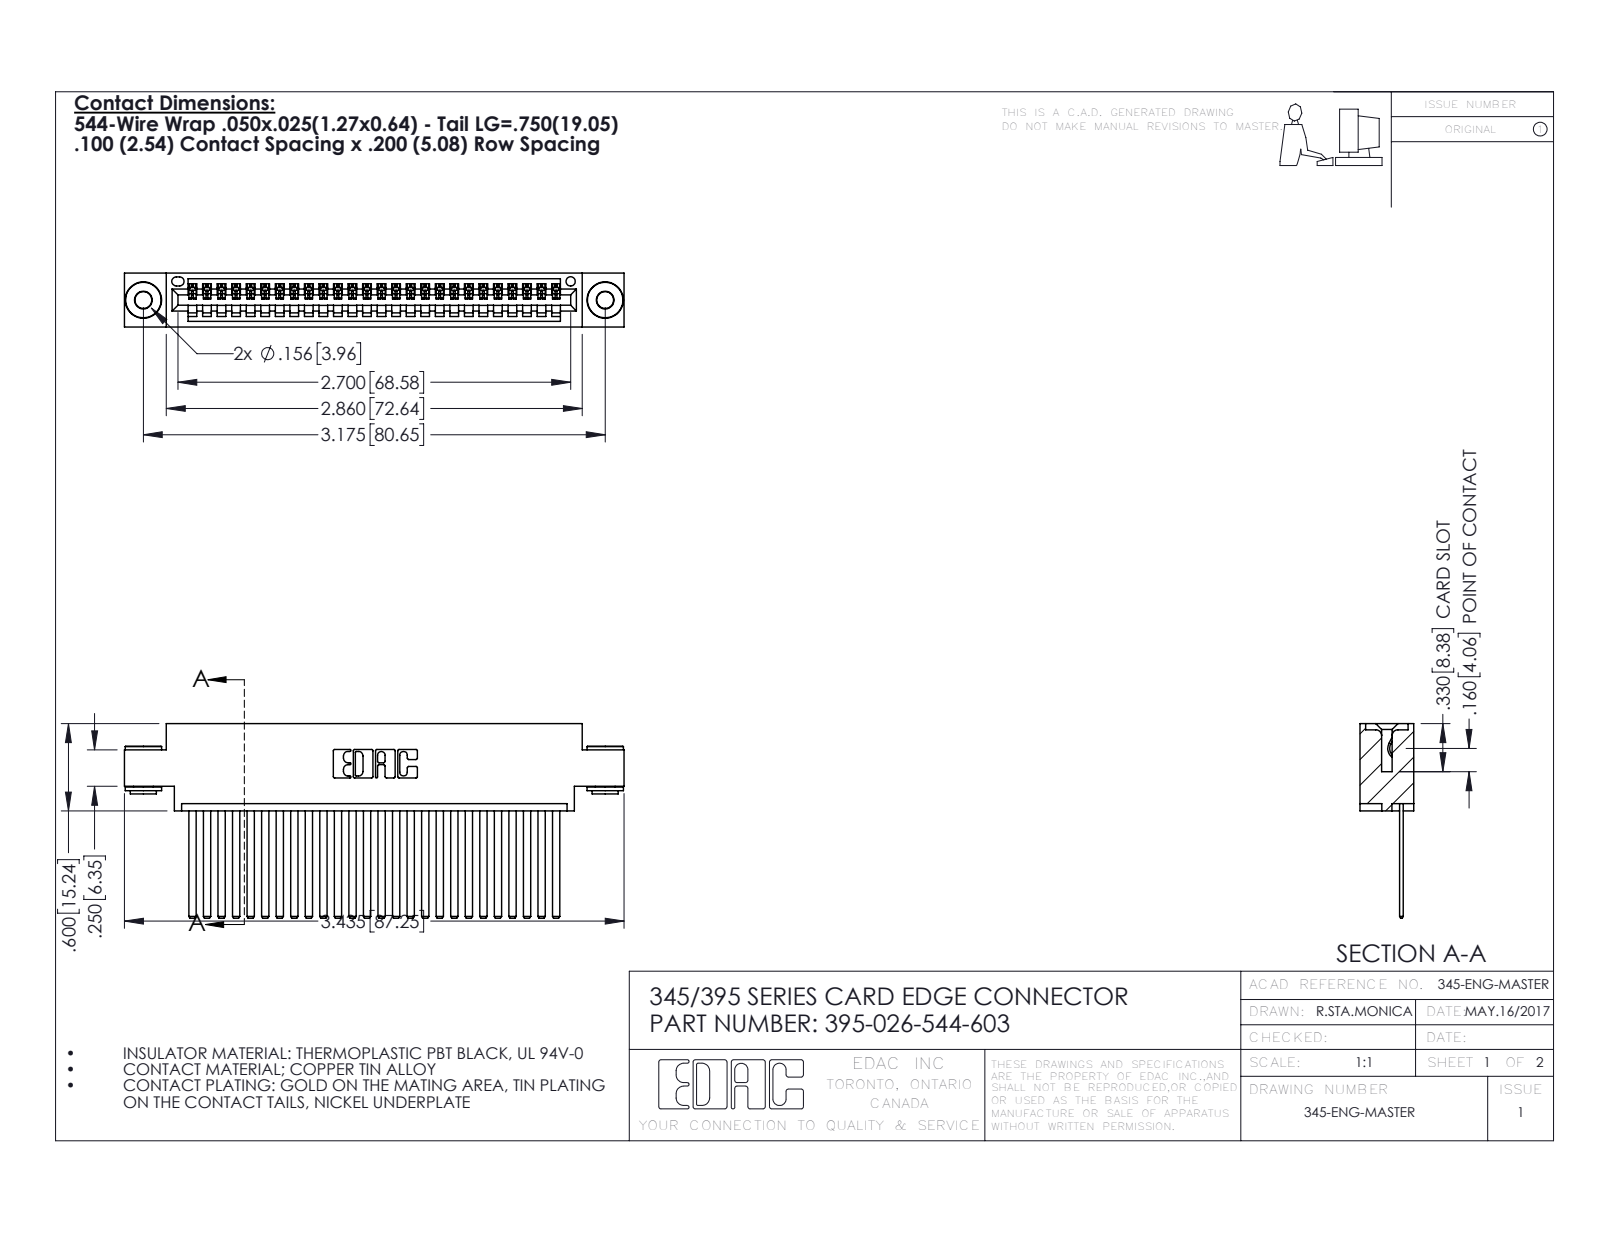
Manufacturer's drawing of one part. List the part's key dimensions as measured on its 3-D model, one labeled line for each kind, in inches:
Part name (STEP PRODUCT): 395-026-544-603; 345-250-002_345-250-002-102; 345-292-001_345-293-144; 345 Part_0.170 Offset - 0.156 Dia-TH
STEP written by: SolidWorks 2016 (CONFIG_CONTROL_DESIGN)
Units: inches
Bodies: 29 solids, 1520 faces (1030 planar, 482 cylindrical, 8 other)
Overall size (bounding box): 3.435 × 1.337 × 0.37
Volume: 0.51 in³ · Surface area: 18.82 in²
Round holes (diameter × count): ⌀0.116 ×2, ⌀0.156 ×2, ⌀0.064 ×1
Round bosses / shafts (diameter × count): ⌀0.25 ×2, ⌀0.18 ×2, ⌀0.136 ×2
Partial cylindrical surfaces — rounded edges, fillets, slot ends (radius × count): R0.006 ×52, R0.01 ×22, R0.007 ×6, R0.031 ×6, R0.026 ×3, R0.031 ×2, R0.04 ×2, R0.014 ×1
Main face-to-face distances: 0.072, 0.298, 0.098, 0.025, 0.272, 0.37, 0.2, 0.225, 0.175, 0.149
Hole centre spacings: 0.27, 2.94, 3.175
